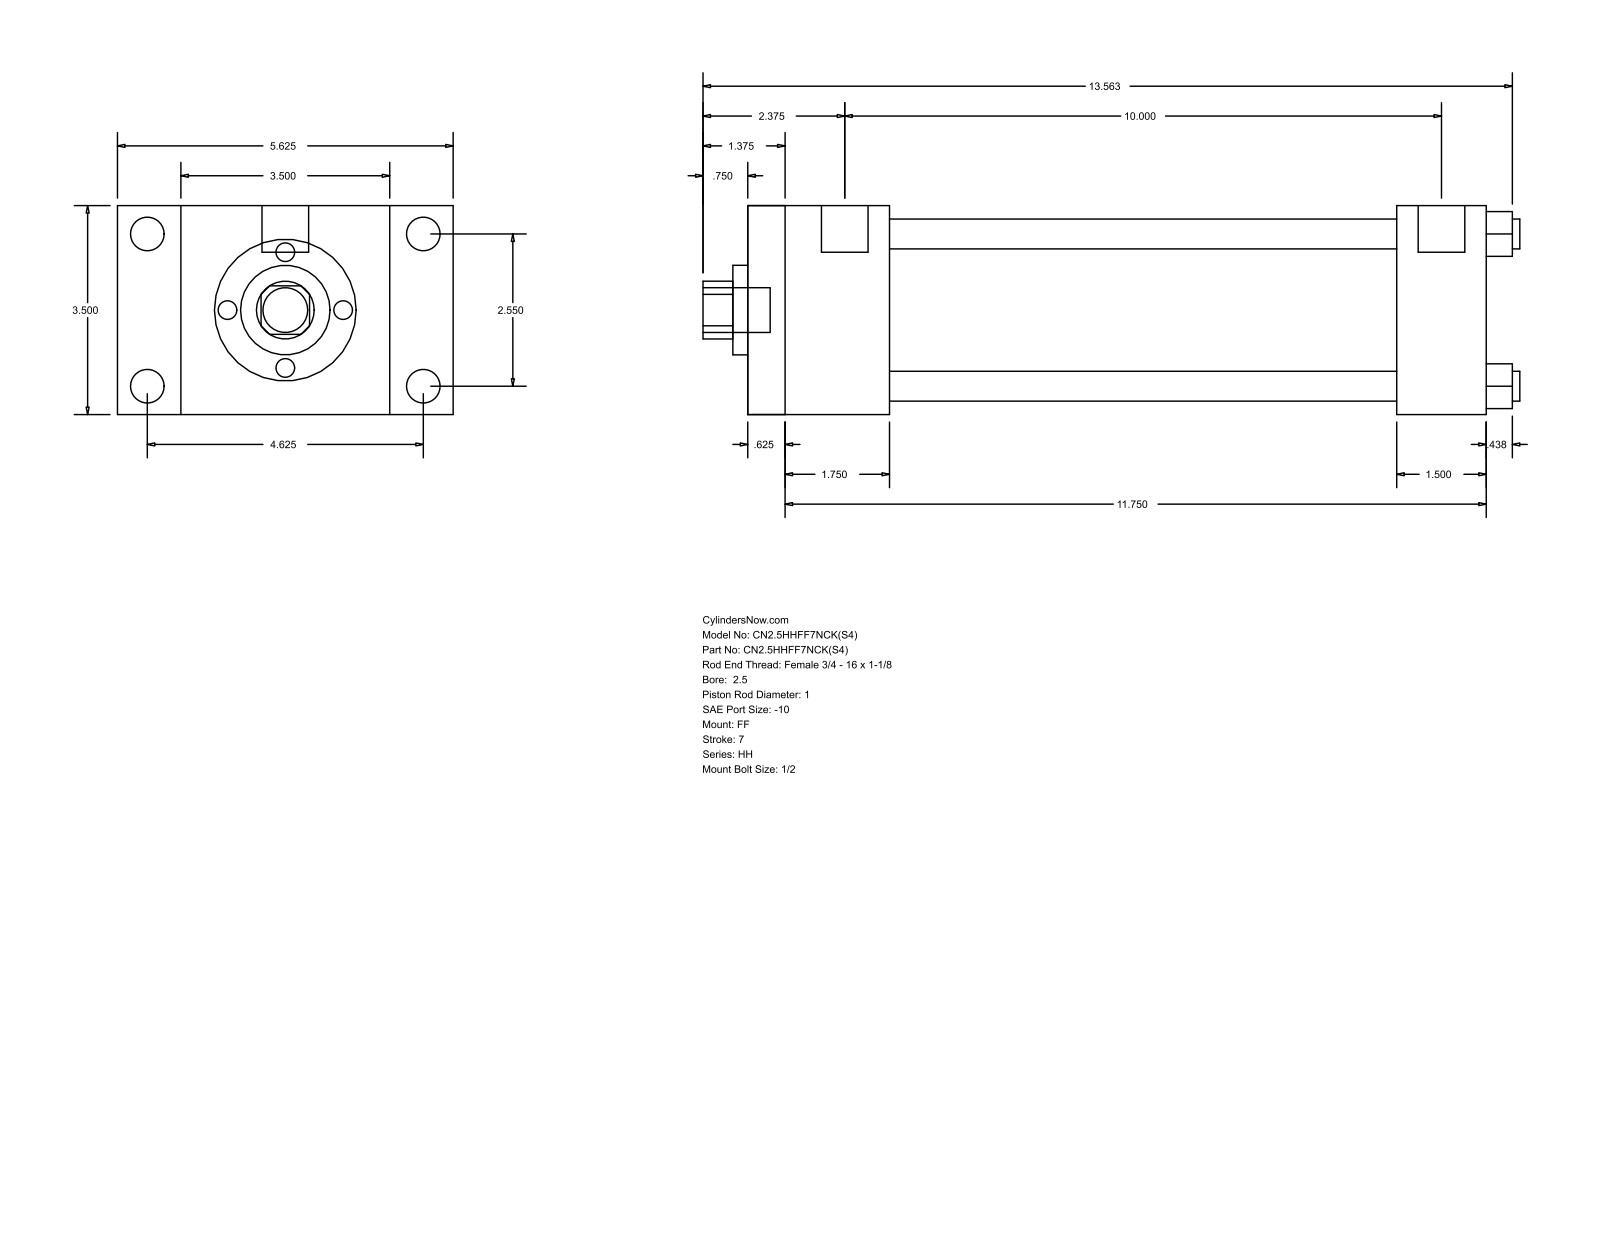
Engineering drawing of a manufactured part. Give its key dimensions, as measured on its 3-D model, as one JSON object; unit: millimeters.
{"part_name": "HH_FF__0250_1", "step_written_by": "GSSL Pune (CONFIG_CONTROL_DESIGN)", "units": "millimeters", "bodies": {"solids": 0, "faces": 92, "planar": 64, "cylindrical": 28, "other": 0}, "overall_size": [347.66, 142.88, 88.9], "round_holes": [[12.7, 4], [25.4, 1], [38.1, 1], [73.03, 1]], "round_bosses_or_shafts": [[14.3, 4], [5.56, 4], [19.84, 2], [19.05, 1]], "partial_cylinders_radius": [[12.29, 1]], "face_to_face_distances": [88.9, 314.33, 15.87, 298.46, 60.33, 44.46, 254, 276.22, 260.35, 215.89], "hole_center_spacings": [45.79, 64.76, 91.58]}
